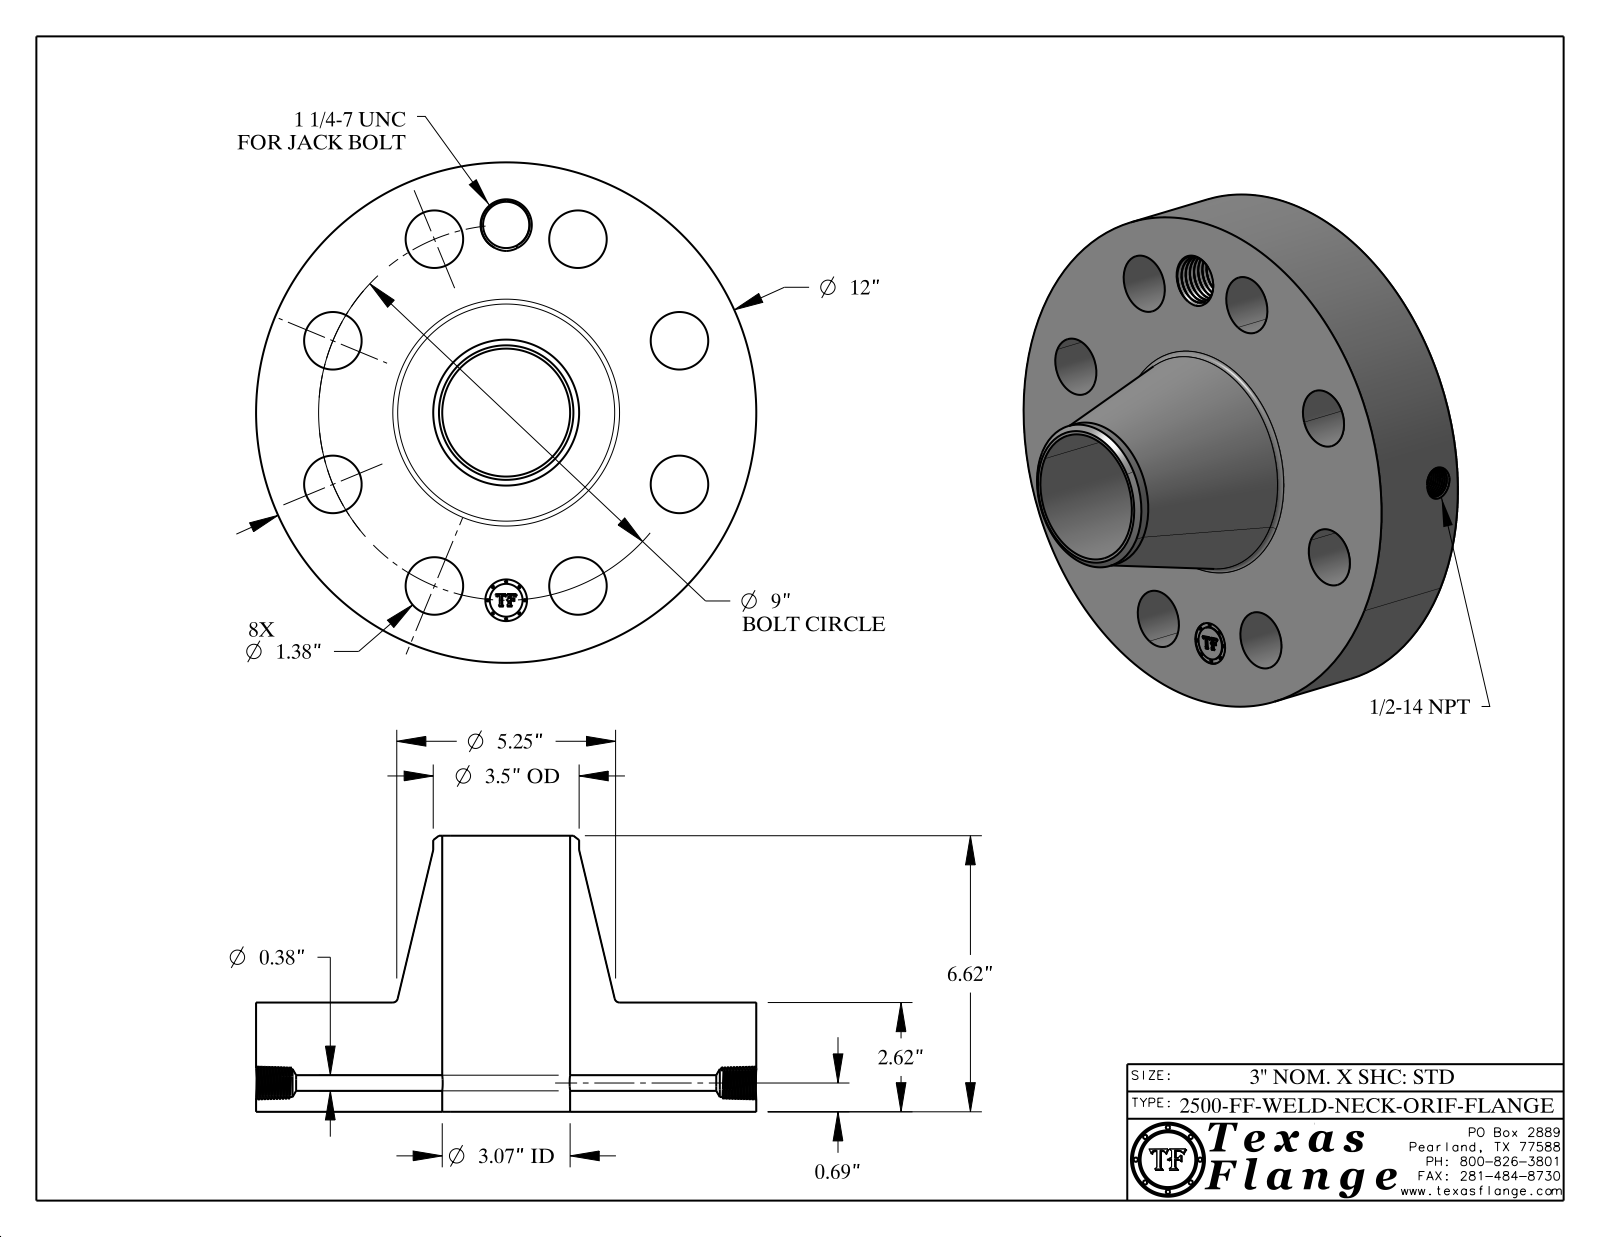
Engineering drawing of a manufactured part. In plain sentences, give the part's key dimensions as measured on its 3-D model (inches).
The part is named "2500-FF-WELD-NECK". Its 3-D file was written by "CATIA V5 STEP AP214 (AUTOMOTIVE_DESIGN)". It is 1 solid with 787 faces: 368 planar, 98 cylindrical and 321 other. Overall it measures 12 by 12 by 6.62 inches. Its volume is 270.6 cubic inches and its surface area 509.5 square inches. Round holes: 8 of diameter 1.38, 1 of diameter 0.375, 1 of diameter 0.672, 1 of diameter 1, 1 of diameter 1.109, 1 of diameter 3.068. Round bosses or shafts: 8 of diameter 0.061, 1 of diameter 12, 1 of diameter 3.5, 1 of diameter 0.788. The main face-to-face distances are 2.62, 6.62, 4, 2.605, 0.015, 4.015, 0.298, 0.293, 0.054, 0.248. The hole center spacings are 4.5, 3.444, 6.364, 8.315, 9, 1.756, 5, 7.483.
